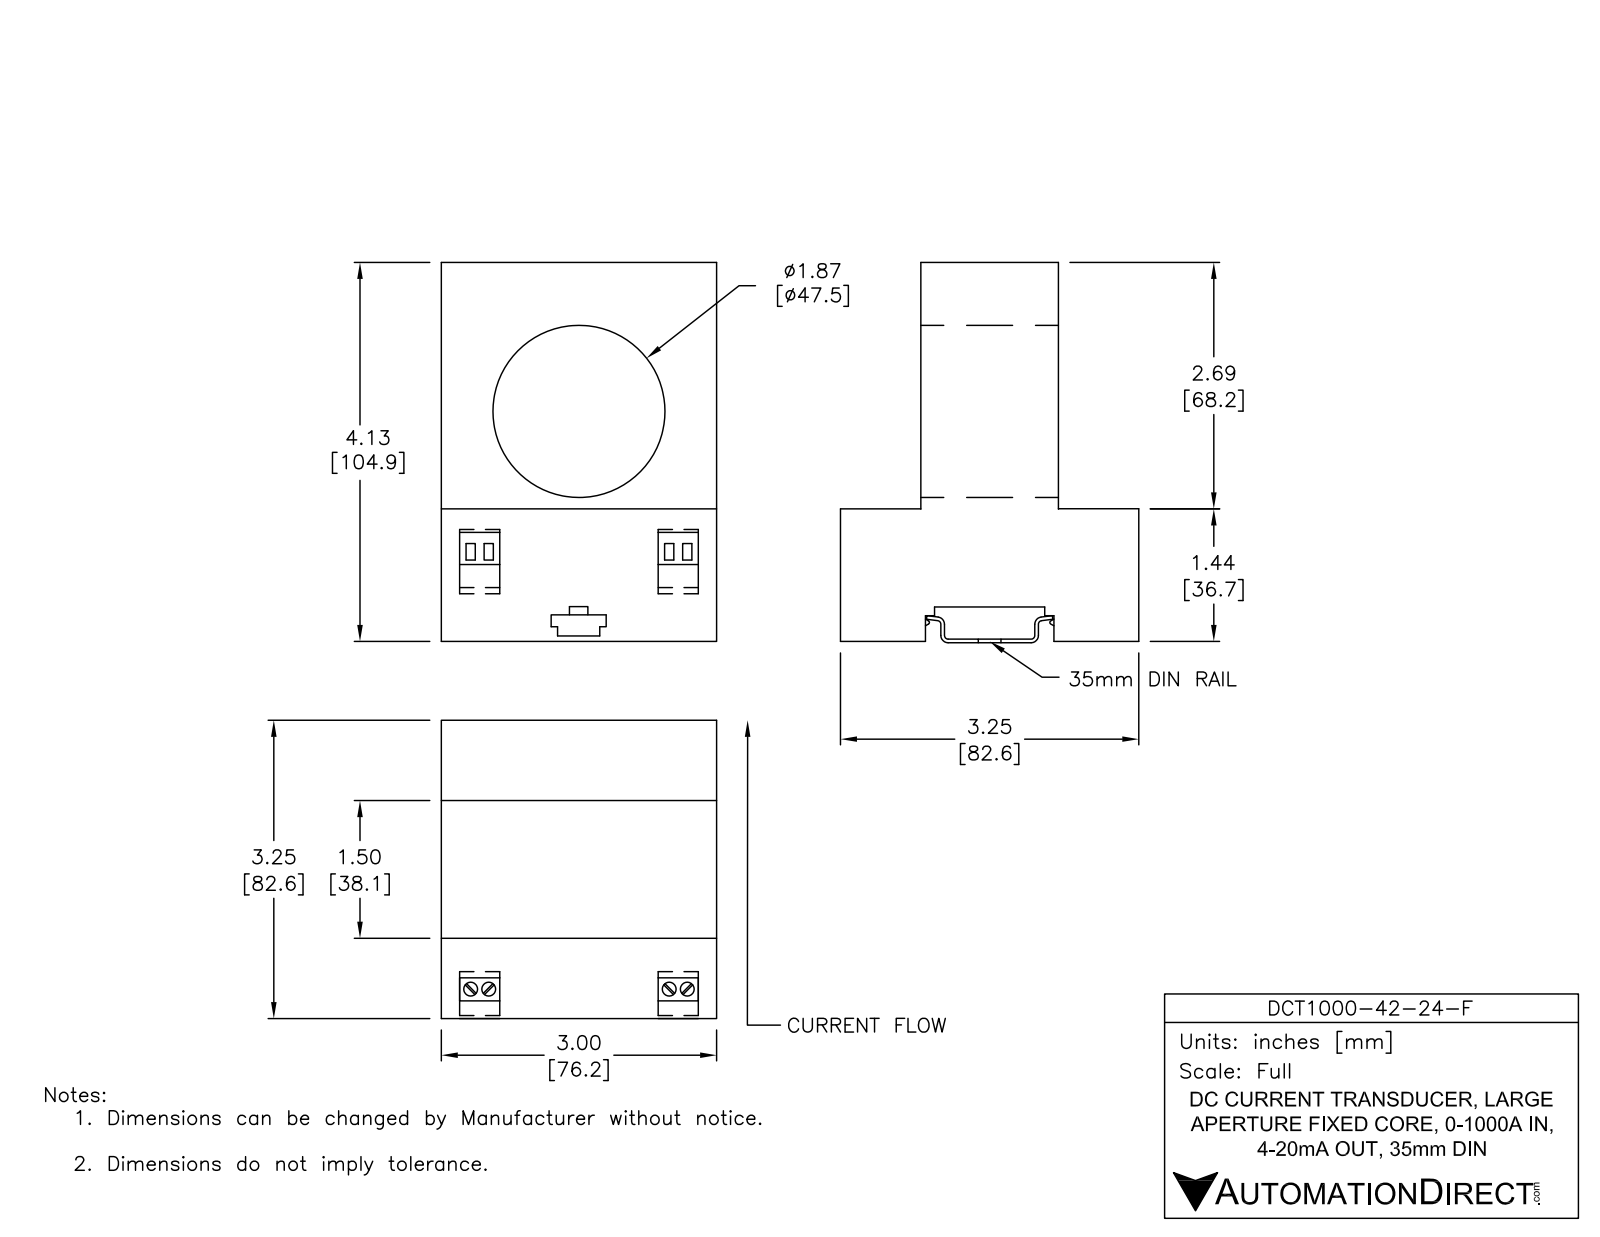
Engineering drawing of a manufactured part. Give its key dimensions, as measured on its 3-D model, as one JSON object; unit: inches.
{"part_name": "DCT1000-42-24-F", "step_written_by": "SolidWorks 2017 (AUTOMOTIVE_DESIGN)", "units": "inches", "bodies": {"solids": 13, "faces": 360, "planar": 310, "cylindrical": 50, "other": 0}, "overall_size": [4.2, 3.524, 3], "volume_in3": 14.05, "surface_area_in2": 110.2, "round_holes": [[0.206, 4], [0.1, 2], [1.82, 1]], "round_bosses_or_shafts": [[0.186, 4]], "partial_cylinders_radius": [[0.099, 4], [0.128, 4], [0.177, 4]], "face_to_face_distances": [0.075, 0.075, 3, 1.206, 1.131, 1.5, 1.25, 1.175, 0.044, 2.37], "hole_center_spacings": [0.394, 1.736, 2.574, 2.704, 0.676, 0.676, 1.068, 1.068]}
